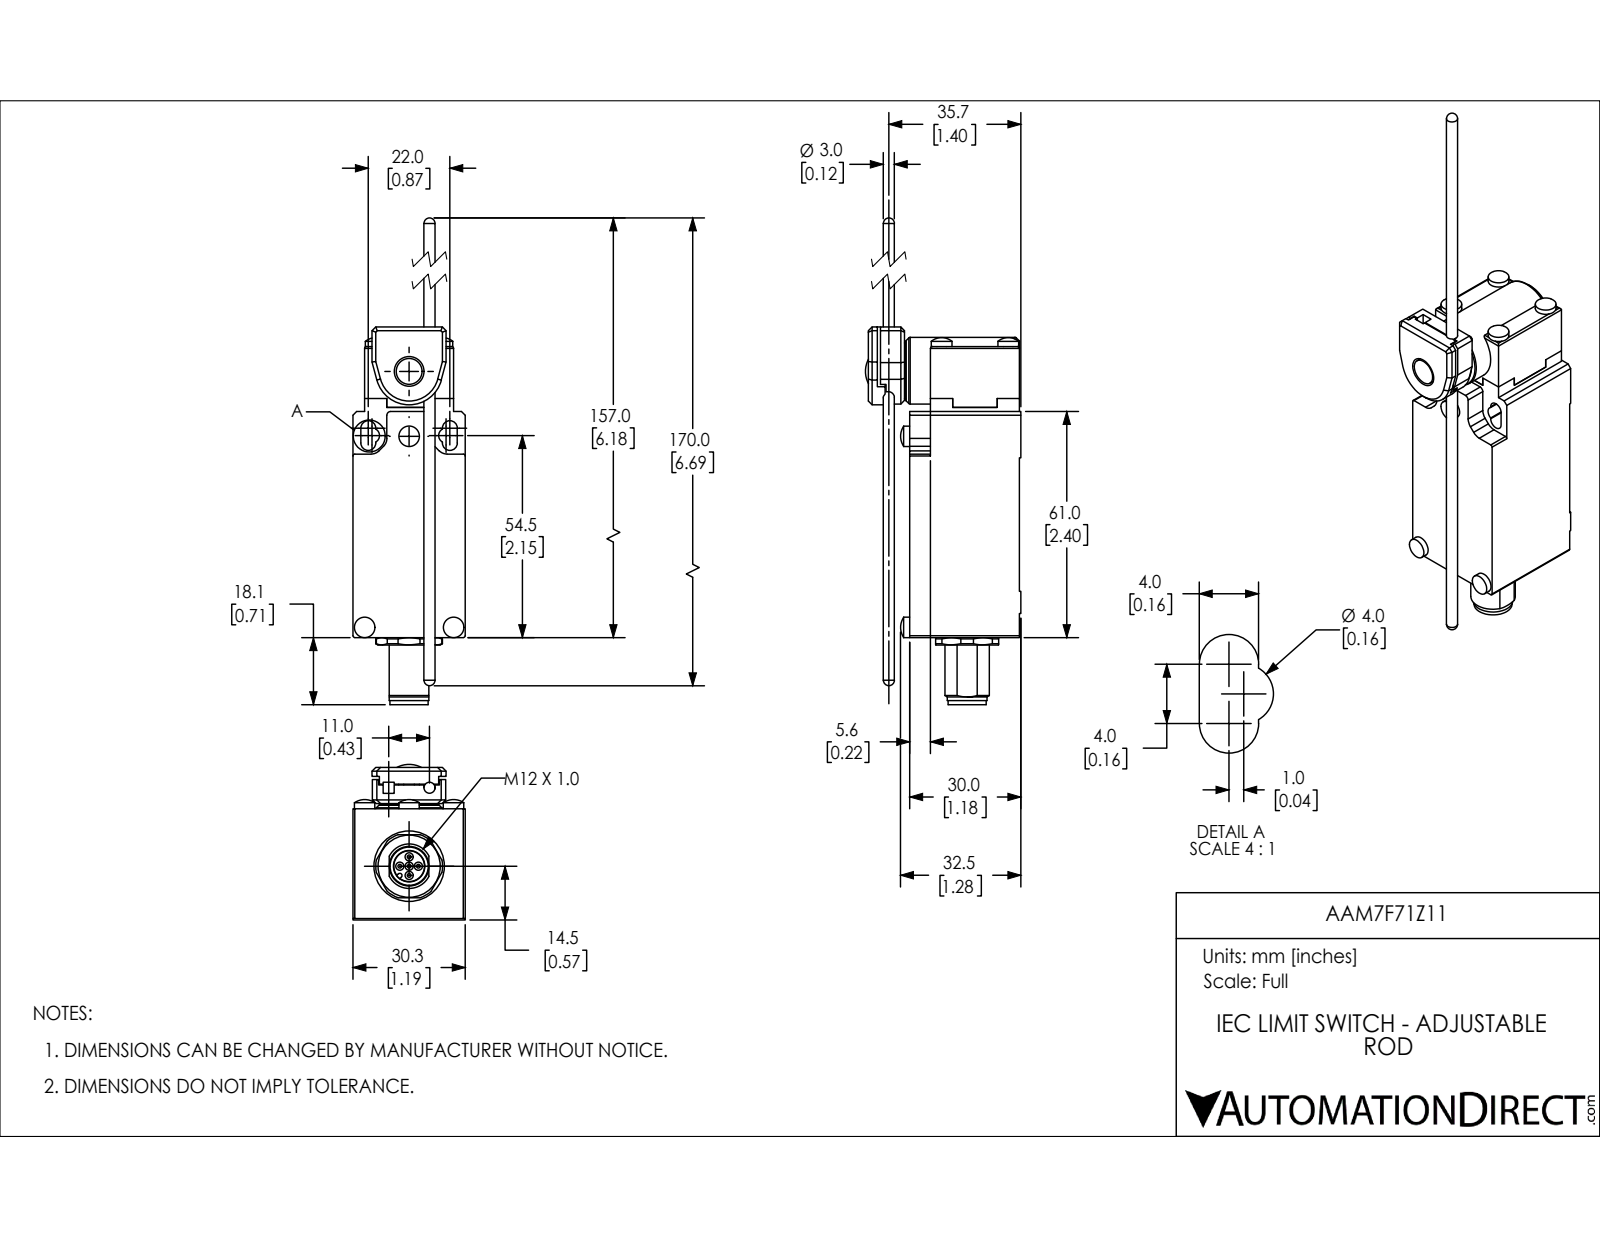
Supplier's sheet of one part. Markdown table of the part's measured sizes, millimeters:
| quantity | value |
| --- | --- |
| part name | AAM7F71Z11 |
| STEP written by | SolidWorks 2018 (AUTOMOTIVE_DESIGN) |
| units | millimeters |
| bodies | 5 solids, 382 faces (184 planar, 140 cylindrical, 58 other) |
| overall size | 175.1 × 42 × 30.3 |
| volume | 71 410 mm³ |
| surface area | 20 450 mm² |
| round holes (diameter × count) | 2.2 × 5, 3 × 1, 8 × 1, 11 × 1, 13 × 1, 14 × 1, 16 × 1 |
| round bosses / shafts (diameter × count) | 1.4 × 5, 1 × 5, 5.6 × 4, 5.5 × 3, 18 × 1, 15 × 1, 10.7 × 1, 10.3 × 1 |
| partial cylindrical surfaces (radius × count) | 0.5 × 8, 2 × 6, 3 × 4, 1 × 2, 9 × 2, 0.6 × 1, 4.6 × 1, 6 × 1 |
| main face-to-face distances | 30.3, 29.6, 3.1, 27.2, 24, 7, 30, 0.4, 1, 6 |
| hole center spacings | 2.5, 3.5, 5, 19.4, 21.8, 21.9, 22.1, 24.4 |
